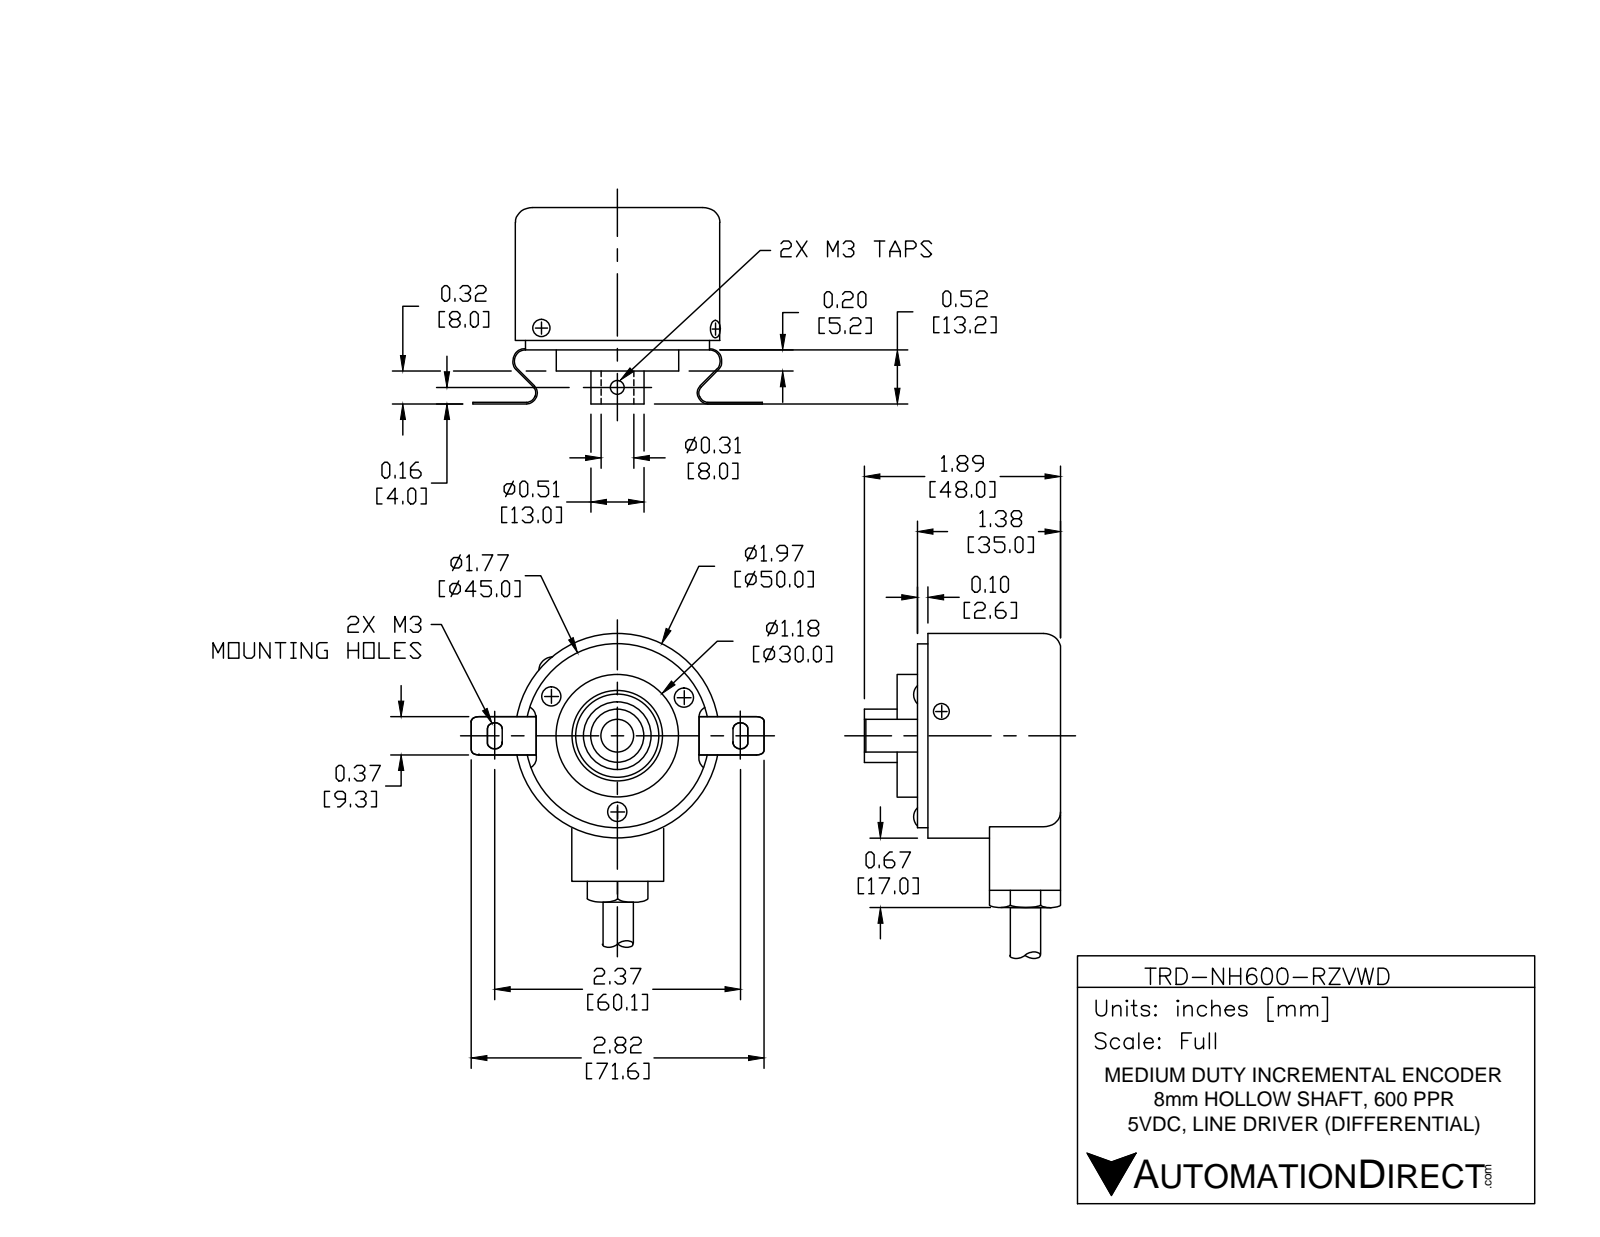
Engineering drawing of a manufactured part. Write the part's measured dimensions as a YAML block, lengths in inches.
part_name: "TRD-NH-RZ"
step_written_by: "SolidWorks 2016 (AUTOMOTIVE_DESIGN)"
units: inches
bodies: {solids: 1, faces: 165, planar: 53, cylindrical: 58, other: 54}
overall_size: [4.654, 2.677, 2.303]
volume: 4.72
surface_area: 22.65
round_holes:
  - {diameter: 0.118, count: 2}
  - {diameter: 0.315, count: 1}
  - {diameter: 0.866, count: 1}
round_bosses_or_shafts:
  - {diameter: 0.236, count: 2}
  - {diameter: 1.772, count: 1}
  - {diameter: 1.181, count: 1}
  - {diameter: 0.512, count: 1}
  - {diameter: 0.433, count: 1}
  - {diameter: 0.394, count: 1}
partial_cylinders:
  - {radius: 0.02, count: 4}
  - {radius: 0.039, count: 4}
  - {radius: 0.071, count: 4}
  - {radius: 0.079, count: 4}
  - {radius: 0.102, count: 4}
  - {radius: 0.118, count: 4}
  - {radius: 0.157, count: 3}
  - {radius: 1.11, count: 1}
face_to_face_distances: [1.453, 0.114, 1.339, 0.016, 0.295, 0.496, 0.024, 0.138, 1.476, 0.157]
